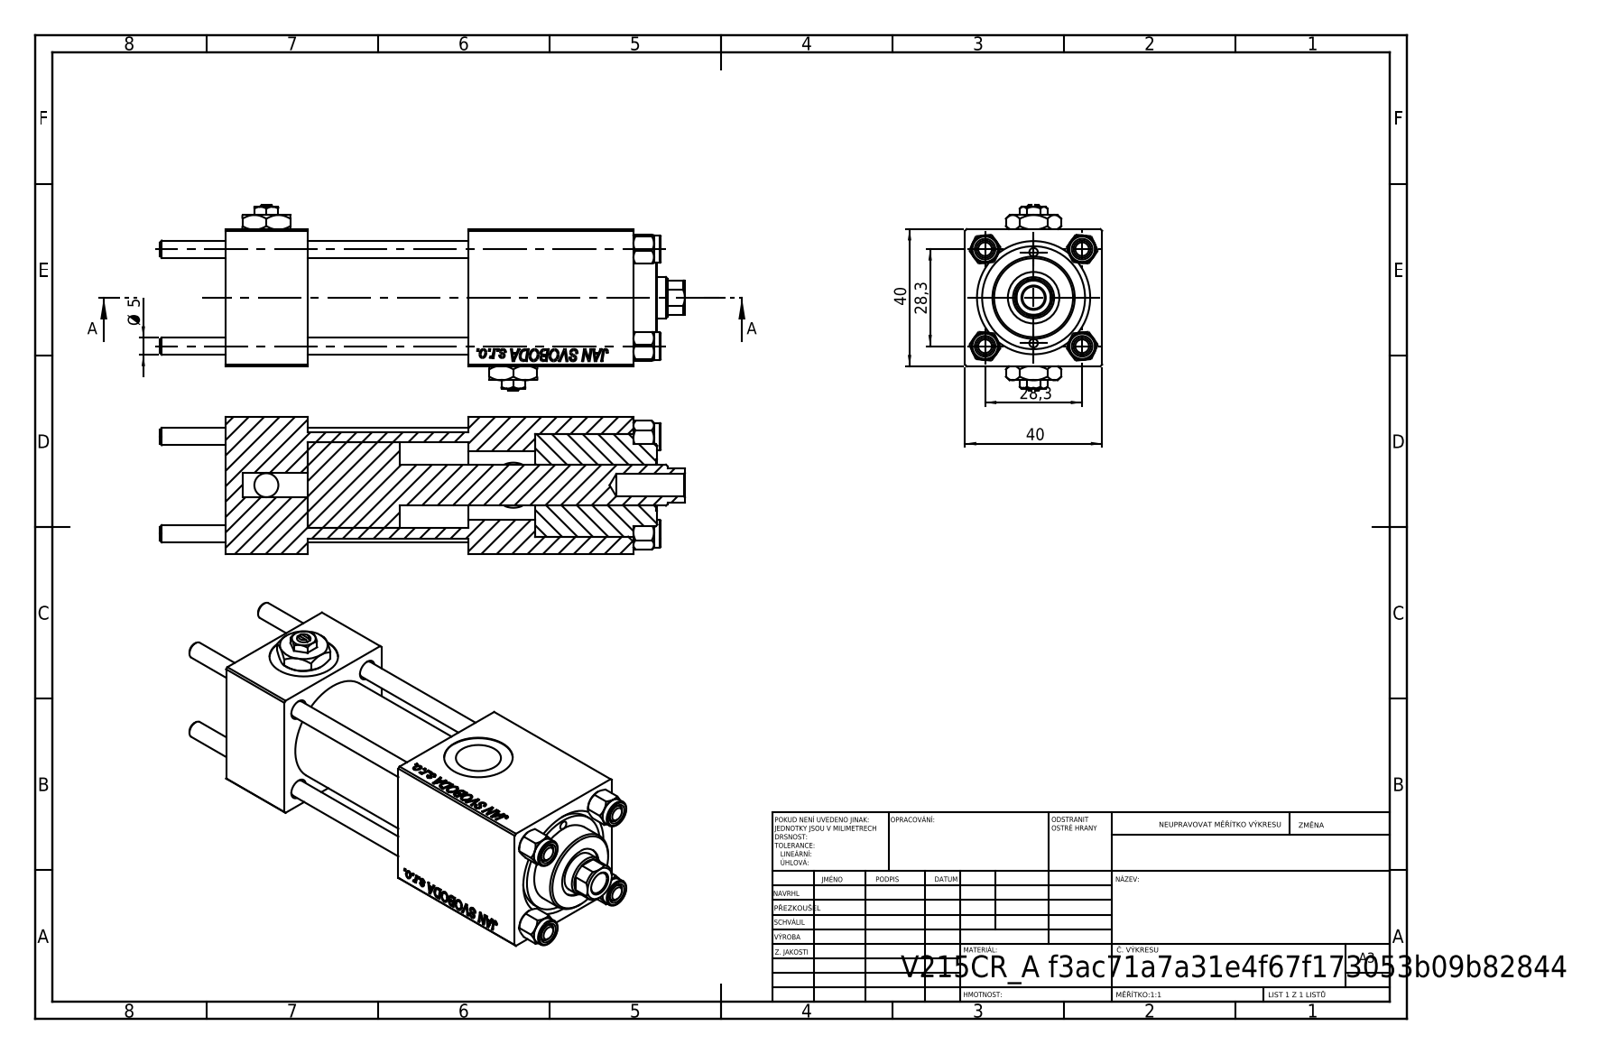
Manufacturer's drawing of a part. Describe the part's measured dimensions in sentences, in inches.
The part is named "Zatka_pro_OIL_PORT; V215_VC_A; CR025_012_A_0_G_A_G_M_020_+#_##_TYCINKA; NUT_M5 (+2 more)". Its 3-D file was written by "SolidWorks 2019 (CONFIG_CONTROL_DESIGN)". It is 13 solids with 1238 faces: 566 planar, 94 cylindrical and 578 other. Overall it measures 6.024 by 2.126 by 1.575 inches. Its volume is 8.749 cubic inches and its surface area 94.11 square inches. Round holes: 4 of diameter 0.197, 3 of diameter 0.787, 2 of diameter 0.098, 2 of diameter 0.276, 2 of diameter 0.518, 1 of diameter 0.256, 1 of diameter 0.472, 1 of diameter 0.591, 1 of diameter 0.984, 1 of diameter 1.181. Round bosses or shafts: 4 of diameter 0.315, 1 of diameter 1.22, 1 of diameter 0.945. Partial cylindrical surfaces (rounded edges, fillets, slot ends): 1 of radius 0.217. The main face-to-face distances are 1.575, 0.945, 1.567, 3.74, 4.685, 3.555, 2.61, 1.13, 1.85, 2.795. The hole center spacings are 0.558, 0.788, 1.114, 1.214, 0.522, 1.576, 1.043, 2.835.
